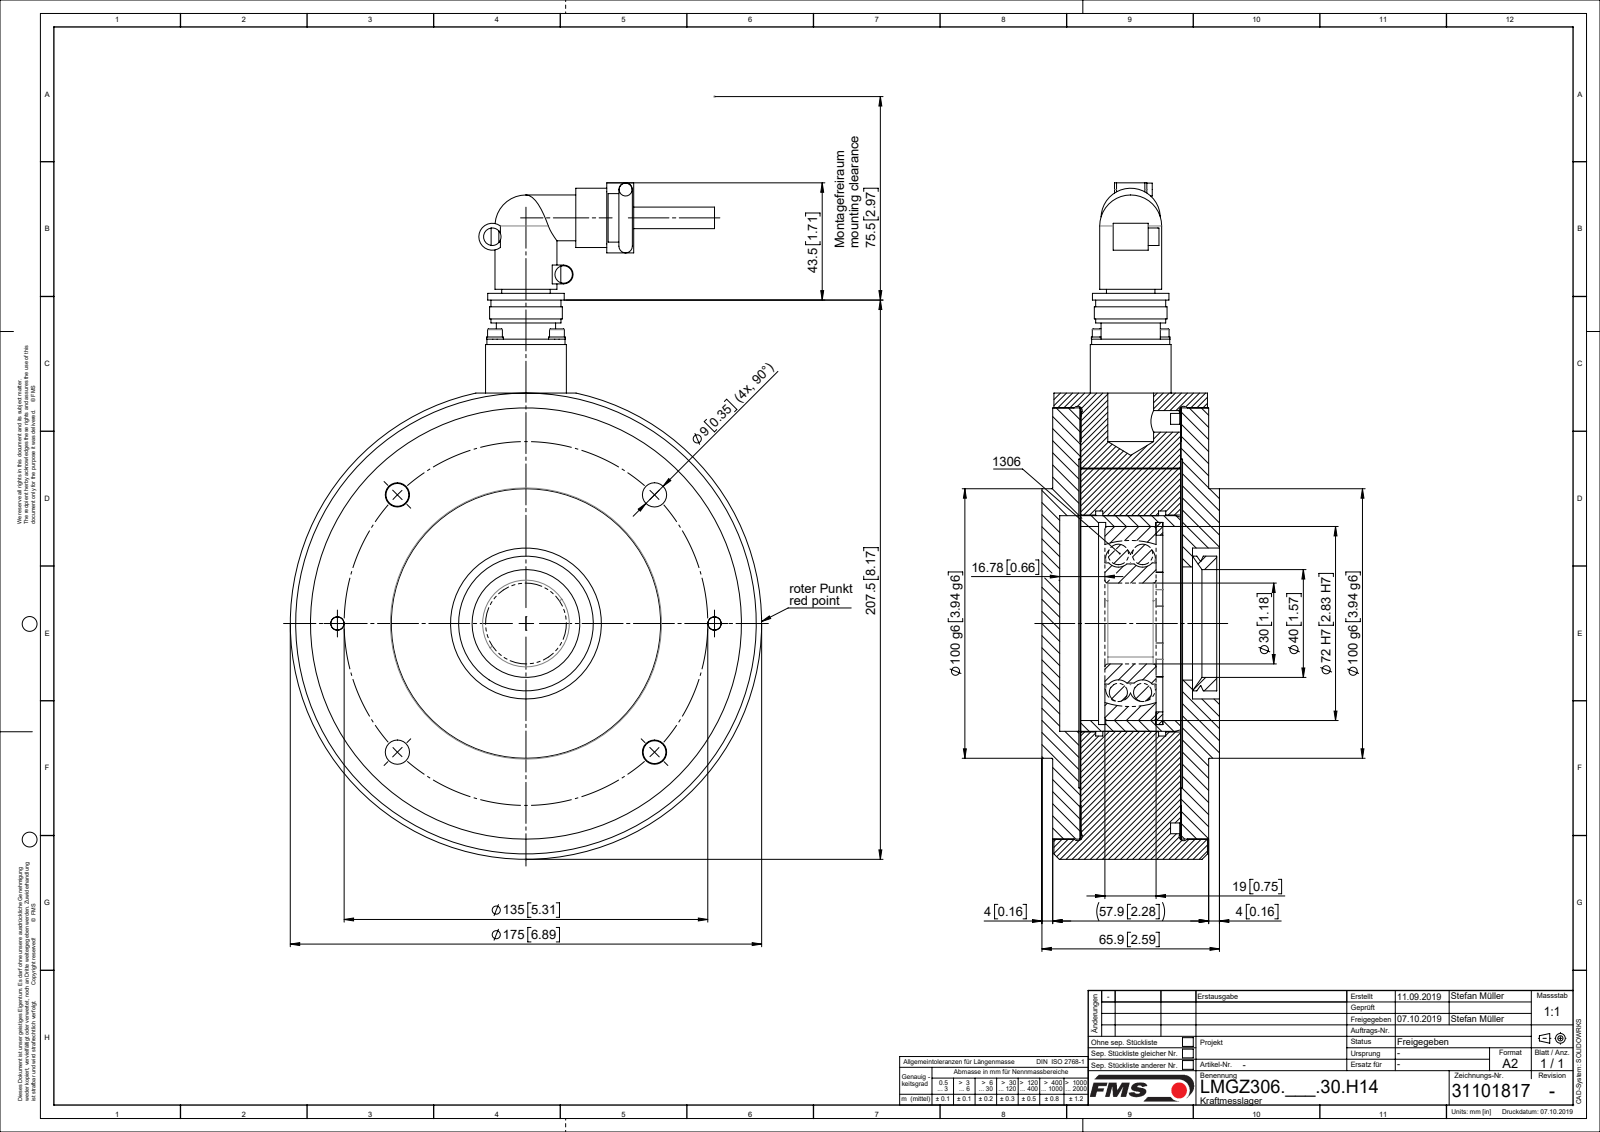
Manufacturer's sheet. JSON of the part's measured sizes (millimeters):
{"part_name": "ZEICHNUNG2; L50324_STP; L4974404; TEIL1 (+8 more)", "step_written_by": "Mechanical Desktop 2009 (CONFIG_CONTROL_DESIGN)", "units": "millimeters", "bodies": {"solids": 22, "faces": 415, "planar": 115, "cylindrical": 239, "other": 61}, "overall_size": [251, 175, 65.9], "volume_mm3": 1295000, "surface_area_mm2": 273519, "round_holes": [[2.6, 4], [3.2, 4], [3.4, 4], [3.5, 4], [9, 4], [5, 2], [6.6, 2], [8, 2], [8.68, 2], [11, 2], [10, 1], [17, 1]], "round_bosses_or_shafts": [[6.2, 4], [5.5, 4], [3, 4], [22, 2], [10, 2], [6.5, 2], [6, 2], [4.8, 2]], "partial_cylinders_radius": [[2.5, 2], [7.5, 2], [3.5, 1], [5, 1]], "face_to_face_distances": [37.25, 10.2, 10.45, 47.45, 47.7, 38, 37, 0.5, 9.7, 48.2], "hole_center_spacings": [16.26, 23, 48.72, 52.67, 67.5, 95.46, 115.55, 127.04]}
